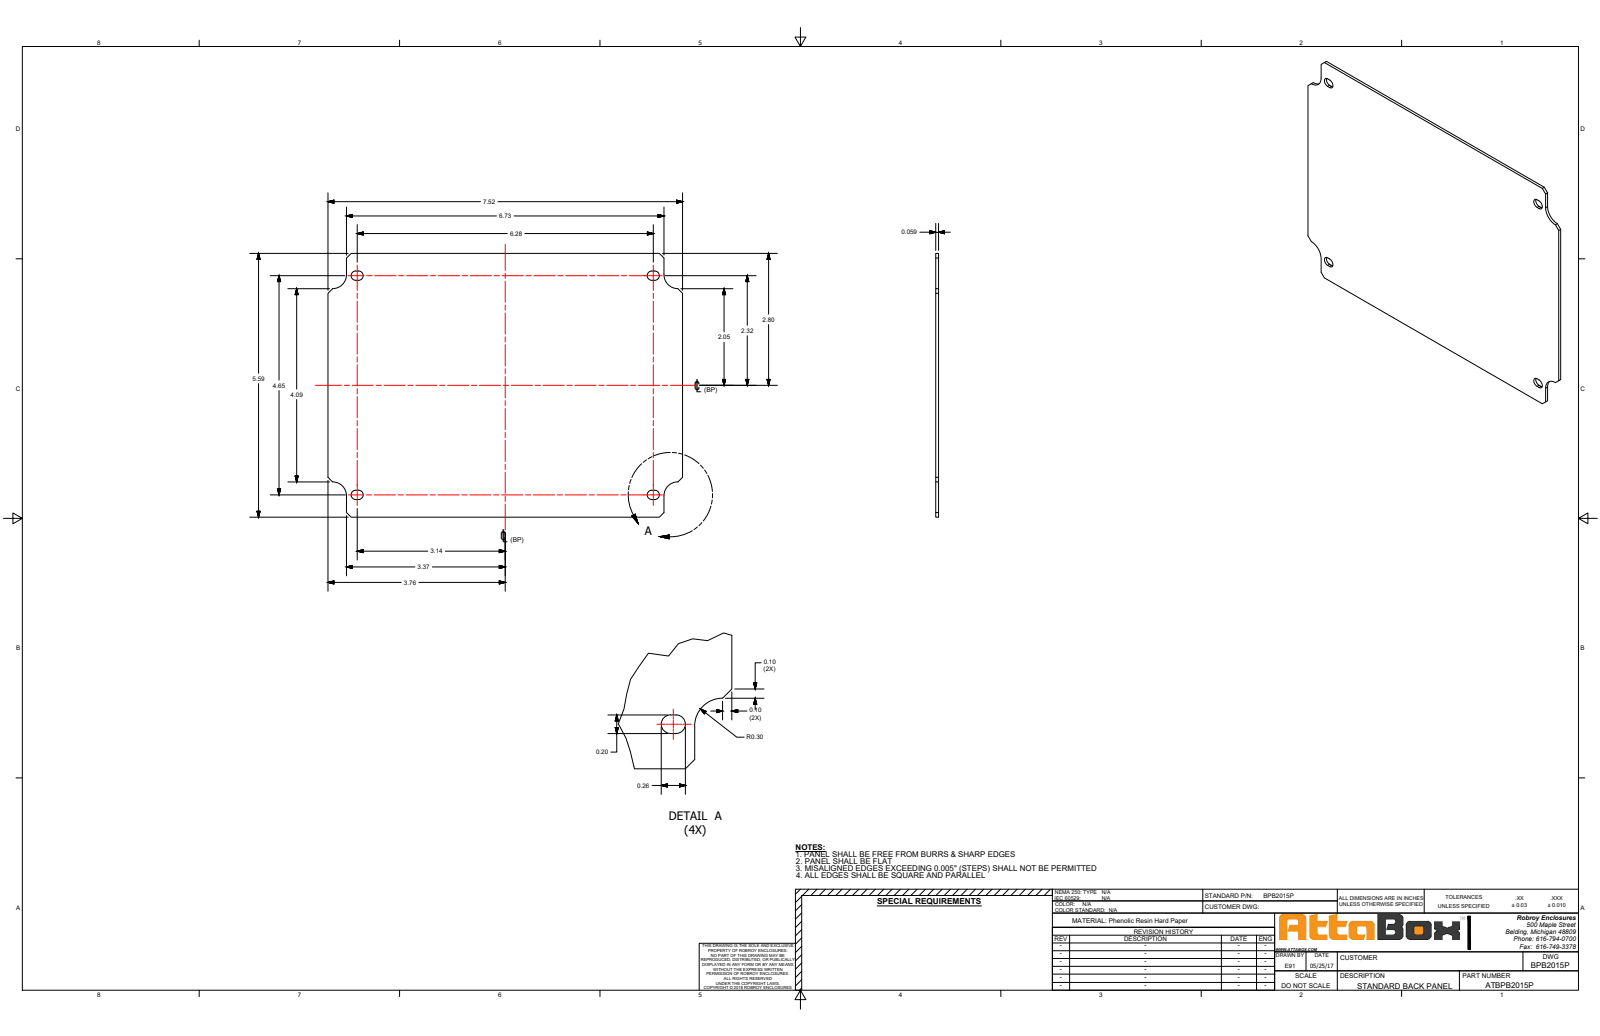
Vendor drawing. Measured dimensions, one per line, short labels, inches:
name: BPB2015P
written by: SolidWorks 2018 (AUTOMOTIVE_DESIGN)
unit: in
bodies: 1 solid, 38 faces (26 planar, 12 cylindrical, 0 other)
size: 7.52 × 5.591 × 0.059
volume: 2.405 in³; area: 83.12 in²
rounds: 8× R0.098, 4× R0.295
face distances: 0.059, 5.591, 7.52, 0.394, 7.126, 6.732, 0.251, 8.322, 8.573, 8.072
